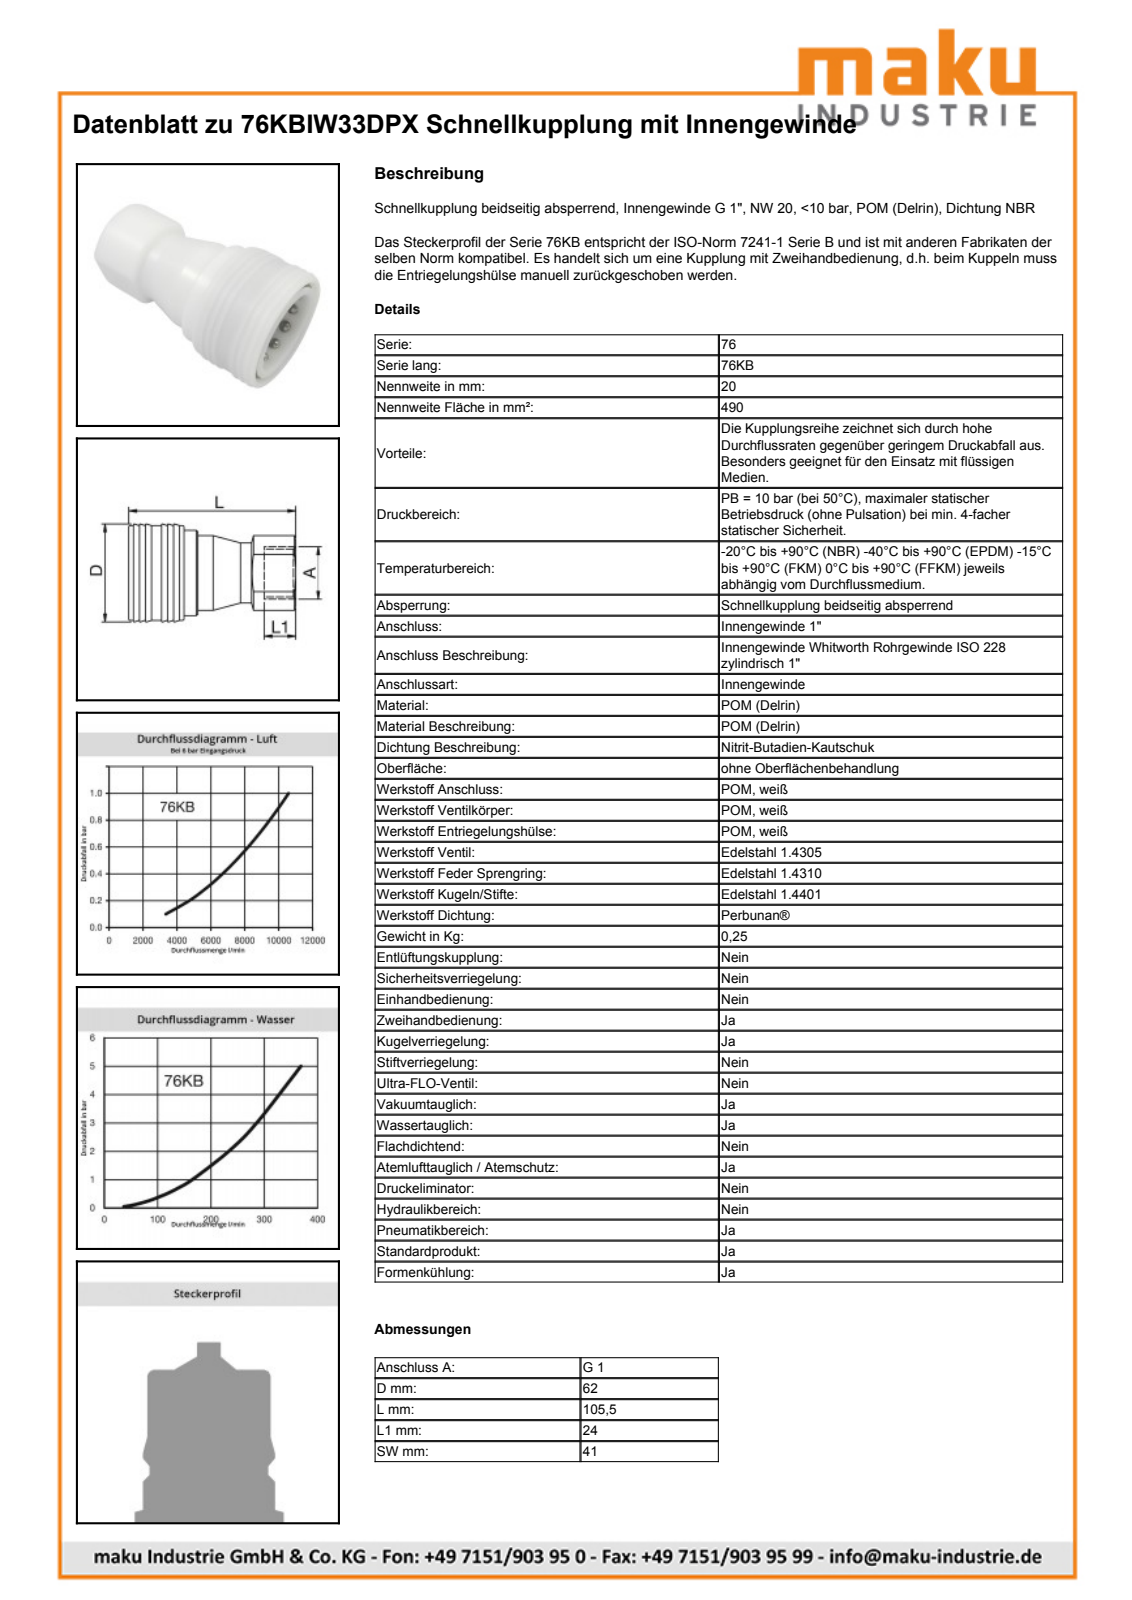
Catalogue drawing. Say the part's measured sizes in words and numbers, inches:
The part is named "D113671". Its 3-D file was written by "Autodesk Inventor 2013 (AUTOMOTIVE_DESIGN)". It is 2 solids with 93 faces: 20 planar, 15 cylindrical and 58 other. Overall it measures 4.157 by 2.441 by 2.441 inches. Its volume is 11.41 cubic inches and its surface area 60.86 square inches. Round holes: 1 of diameter 1.193, 1 of diameter 1.949, 1 of diameter 2.126, 1 of diameter 2.142. Round bosses or shafts: 1 of diameter 2.362, 1 of diameter 1.929, 1 of diameter 1.862, 1 of diameter 1.823, 1 of diameter 1.496. The main face-to-face distances are 3.204, 1.614, 0.954, 4.157, 2.441, 1.487, 1.717, 2.917, 1.963, 0.476.
